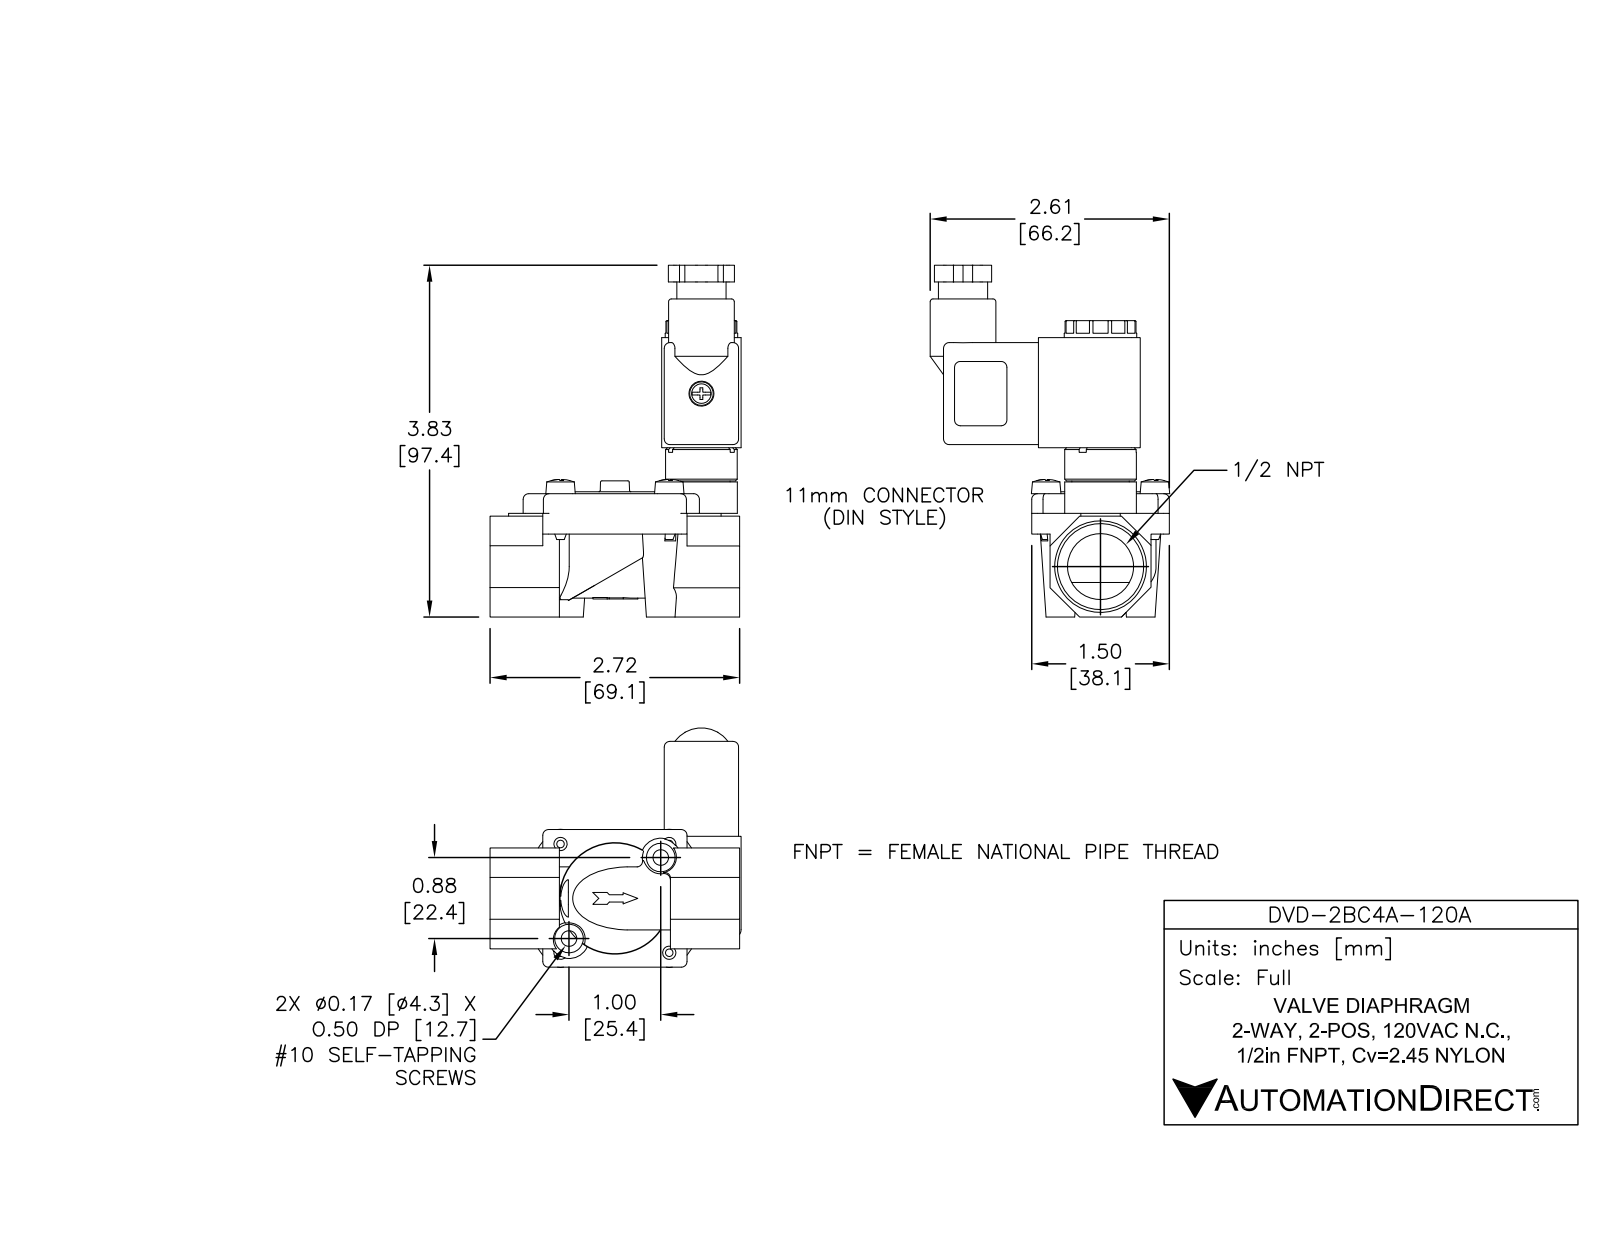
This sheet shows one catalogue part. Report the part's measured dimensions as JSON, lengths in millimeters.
{"part_name": "DVD-2BC4A-120A", "step_written_by": "SolidWorks 2015 (AUTOMOTIVE_DESIGN)", "units": "millimeters", "bodies": {"solids": 13, "faces": 1449, "planar": 725, "cylindrical": 257, "other": 467}, "overall_size": [97.4, 69.5, 66.3], "volume_mm3": 63170, "surface_area_mm2": 39740, "round_holes": [[3.7, 4], [4.2, 4], [1.5, 2], [2.4, 2], [4.3, 2], [17.9, 2], [1.6, 1], [4, 1], [4.2, 1], [6.4, 1], [6.9, 1], [7.9, 1]], "round_bosses_or_shafts": [[4.7, 4], [3.2, 4], [15.9, 2], [34.9, 1], [20.1, 1], [19.9, 1], [19.8, 1], [18.2, 1]], "partial_cylinders_radius": [[0.3, 24], [1.6, 24], [4, 12], [1.1, 3], [2.4, 2], [5.5, 2], [8, 1], [8.7, 1]], "face_to_face_distances": [1.3, 27.9, 22, 19.3, 5.1, 33, 20, 2, 2, 18], "hole_center_spacings": [21.3, 30.1, 4.6, 16.9, 17.5, 26.3, 28, 38.2]}
